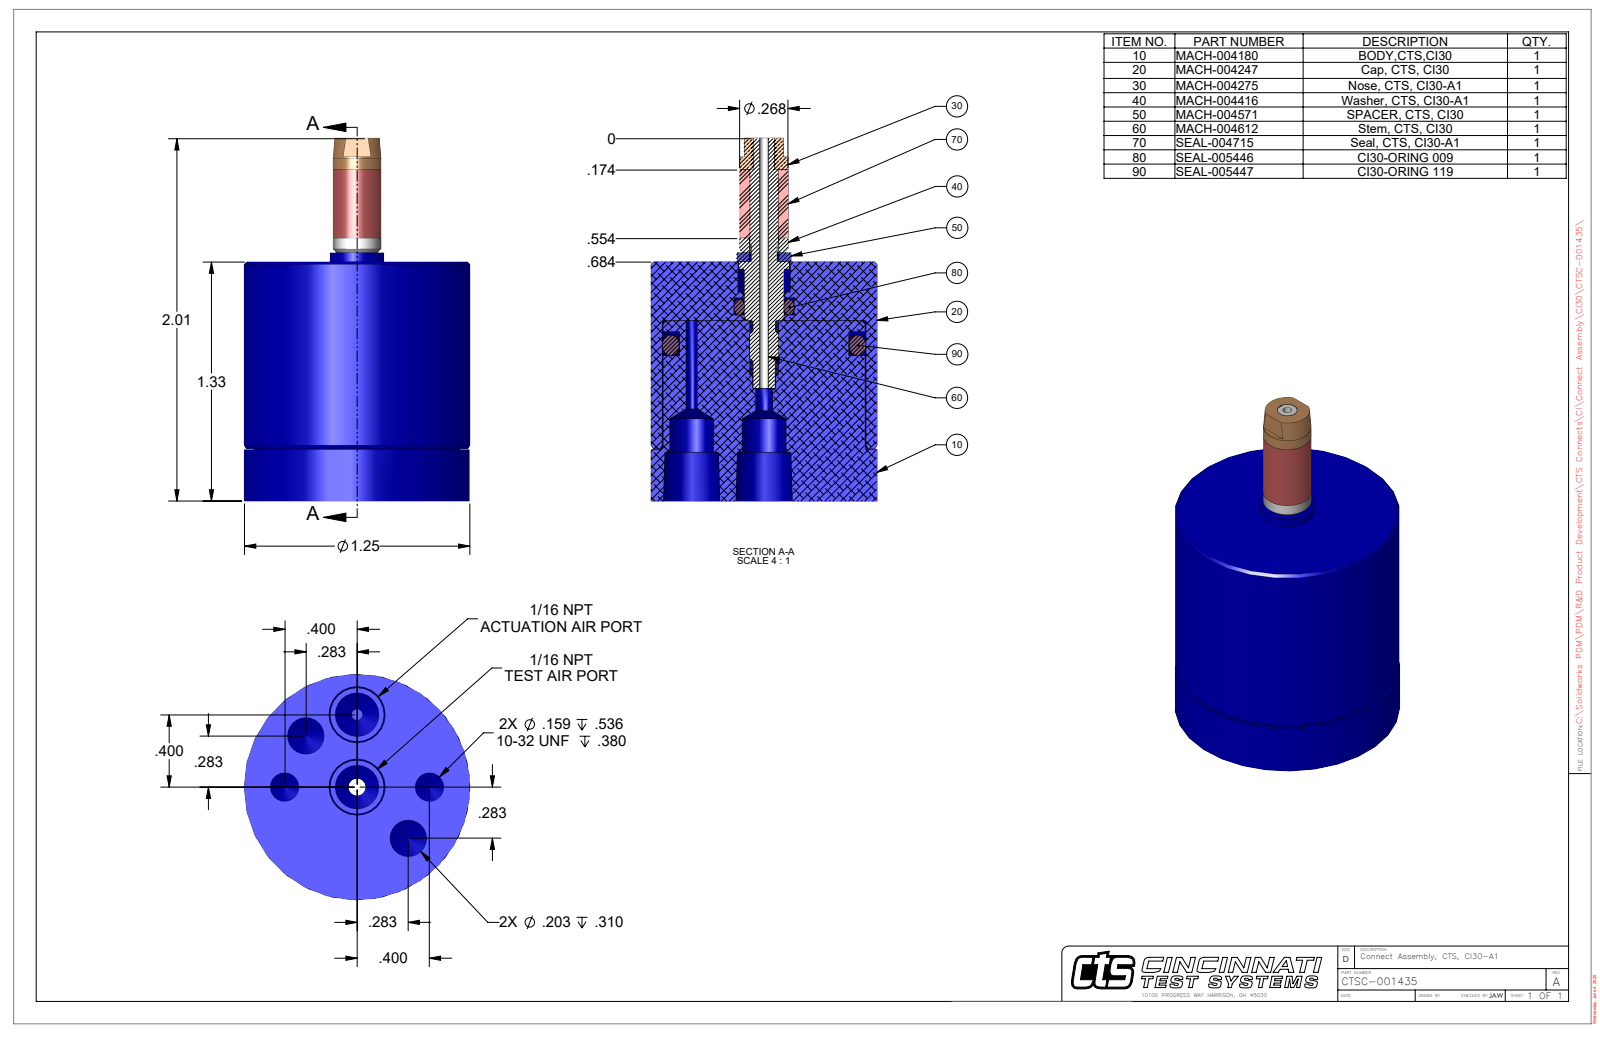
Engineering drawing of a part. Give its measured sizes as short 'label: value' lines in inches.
name: CTSC-001435
written by: SolidWorks 2023 (AUTOMOTIVE_DESIGN)
unit: in
bodies: 1 solid, 79 faces (17 planar, 34 cylindrical, 28 other)
size: 2.009 × 1.25 × 1.25
volume: 1.55 in³; area: 13.03 in²
holes: 2× ⌀0.159, 2× ⌀0.203, 2× ⌀0.242, 1× ⌀0.052, 1× ⌀0.062, 1× ⌀0.094, 1× ⌀0.289, 1× ⌀1.125
bosses: 1× ⌀1.25, 1× ⌀1.115, 1× ⌀0.3, 1× ⌀0.277, 1× ⌀0.268
face distances: 1.325, 0.287, 1.039, 0.29, 1.035, 0.271, 0.015, 0.019, 1.054, 2.009
hole spacings: 0.306, 0.4, 0.739, 0.4, 0.566, 0.8, 0.8
